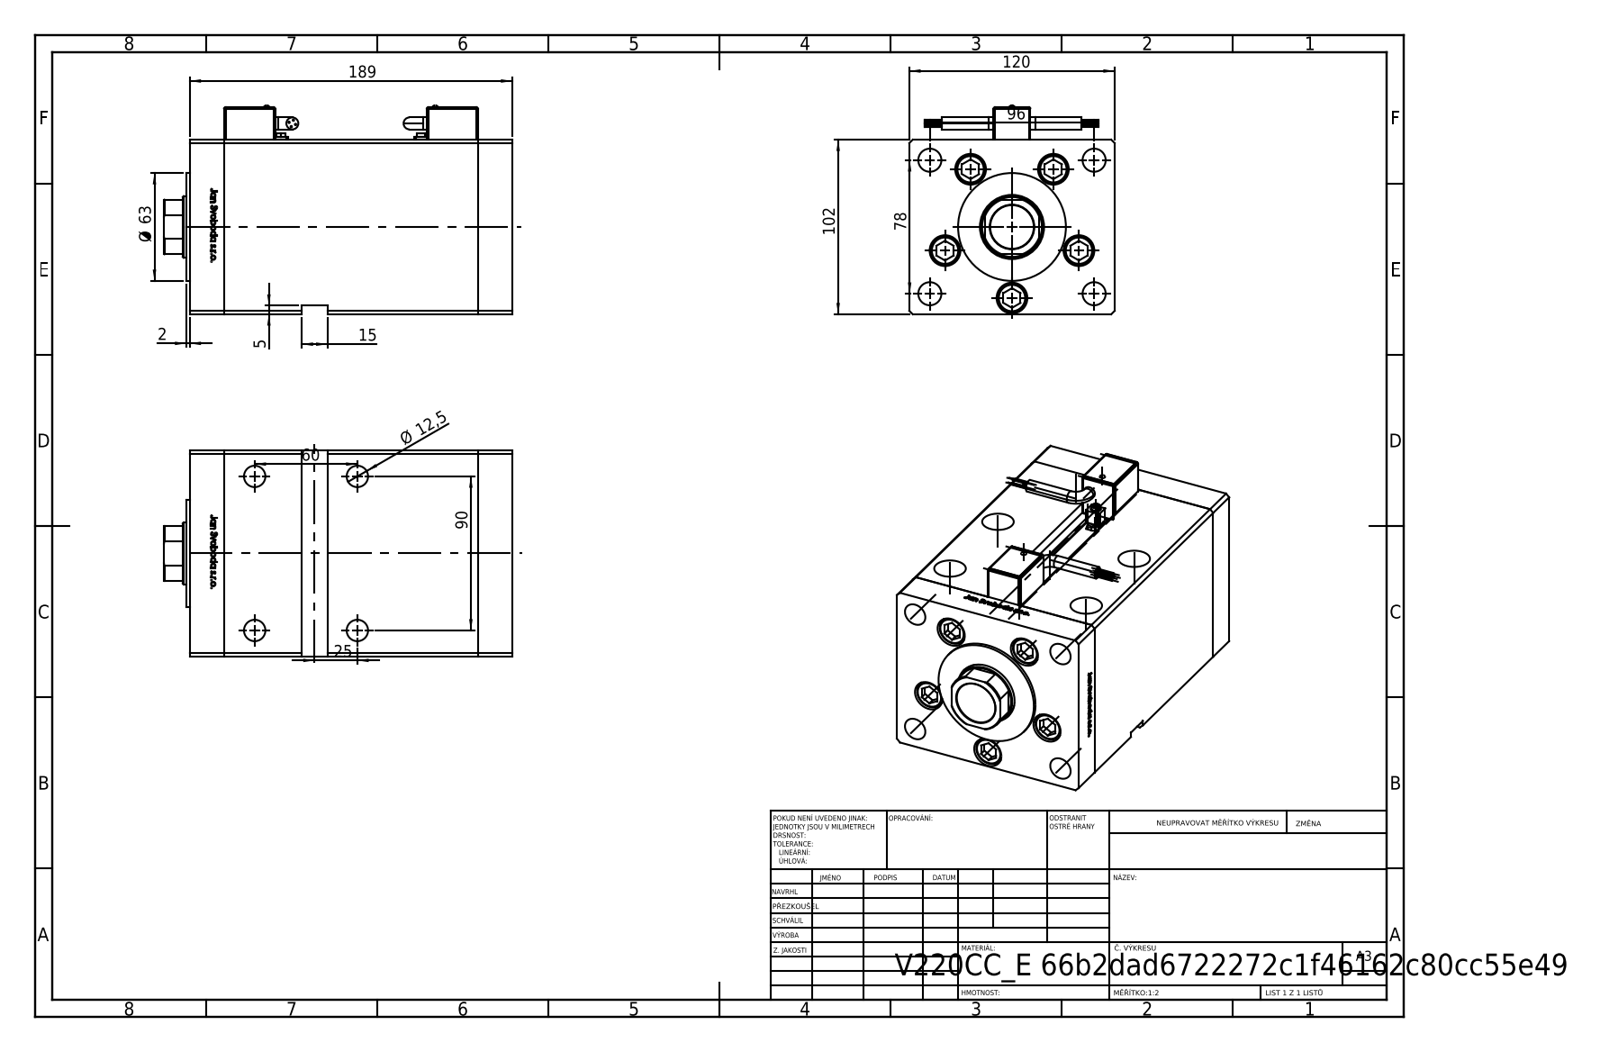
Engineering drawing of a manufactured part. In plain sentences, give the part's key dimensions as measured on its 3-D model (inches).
The part is named "V220C_E MIDDLE; V220C_VC_E; V220C BACK_E; Magnetic_Switch_MSU4 (+2 more)". Its 3-D file was written by "SolidWorks 2019 (CONFIG_CONTROL_DESIGN)". It is 16 solids with 1418 faces: 553 planar, 255 cylindrical and 610 other. Overall it measures 8.012 by 4.807 by 4.724 inches. Its volume is 122.7 cubic inches and its surface area 442.3 square inches. Round holes: 9 of diameter 0.531, 5 of diameter 0.709, 4 of diameter 0.492, 4 of diameter 0.728, 2 of diameter 0.079, 2 of diameter 0.142, 2 of diameter 0.197, 2 of diameter 0.276, 2 of diameter 0.518, 1 of diameter 1.004, 1 of diameter 1.417, 1 of diameter 1.476. Round bosses or shafts: 8 of diameter 0.033, 5 of diameter 0.669, 5 of diameter 0.315, 4 of diameter 0.276, 2 of diameter 0.236, 2 of diameter 0.138, 2 of diameter 0.098, 1 of diameter 2.48. Partial cylindrical surfaces (rounded edges, fillets, slot ends): 24 of radius 0.039, 4 of radius 0.157, 2 of radius 0.037, 1 of radius 0.689. The main face-to-face distances are 4.724, 0.787, 5.846, 6.634, 4.016, 1.348, 7.421, 0.561, 5.285, 6.073. The hole center spacings are 1.634, 2.435, 0.325, 0.96, 1.051, 1.793, 1.87, 1.887.
